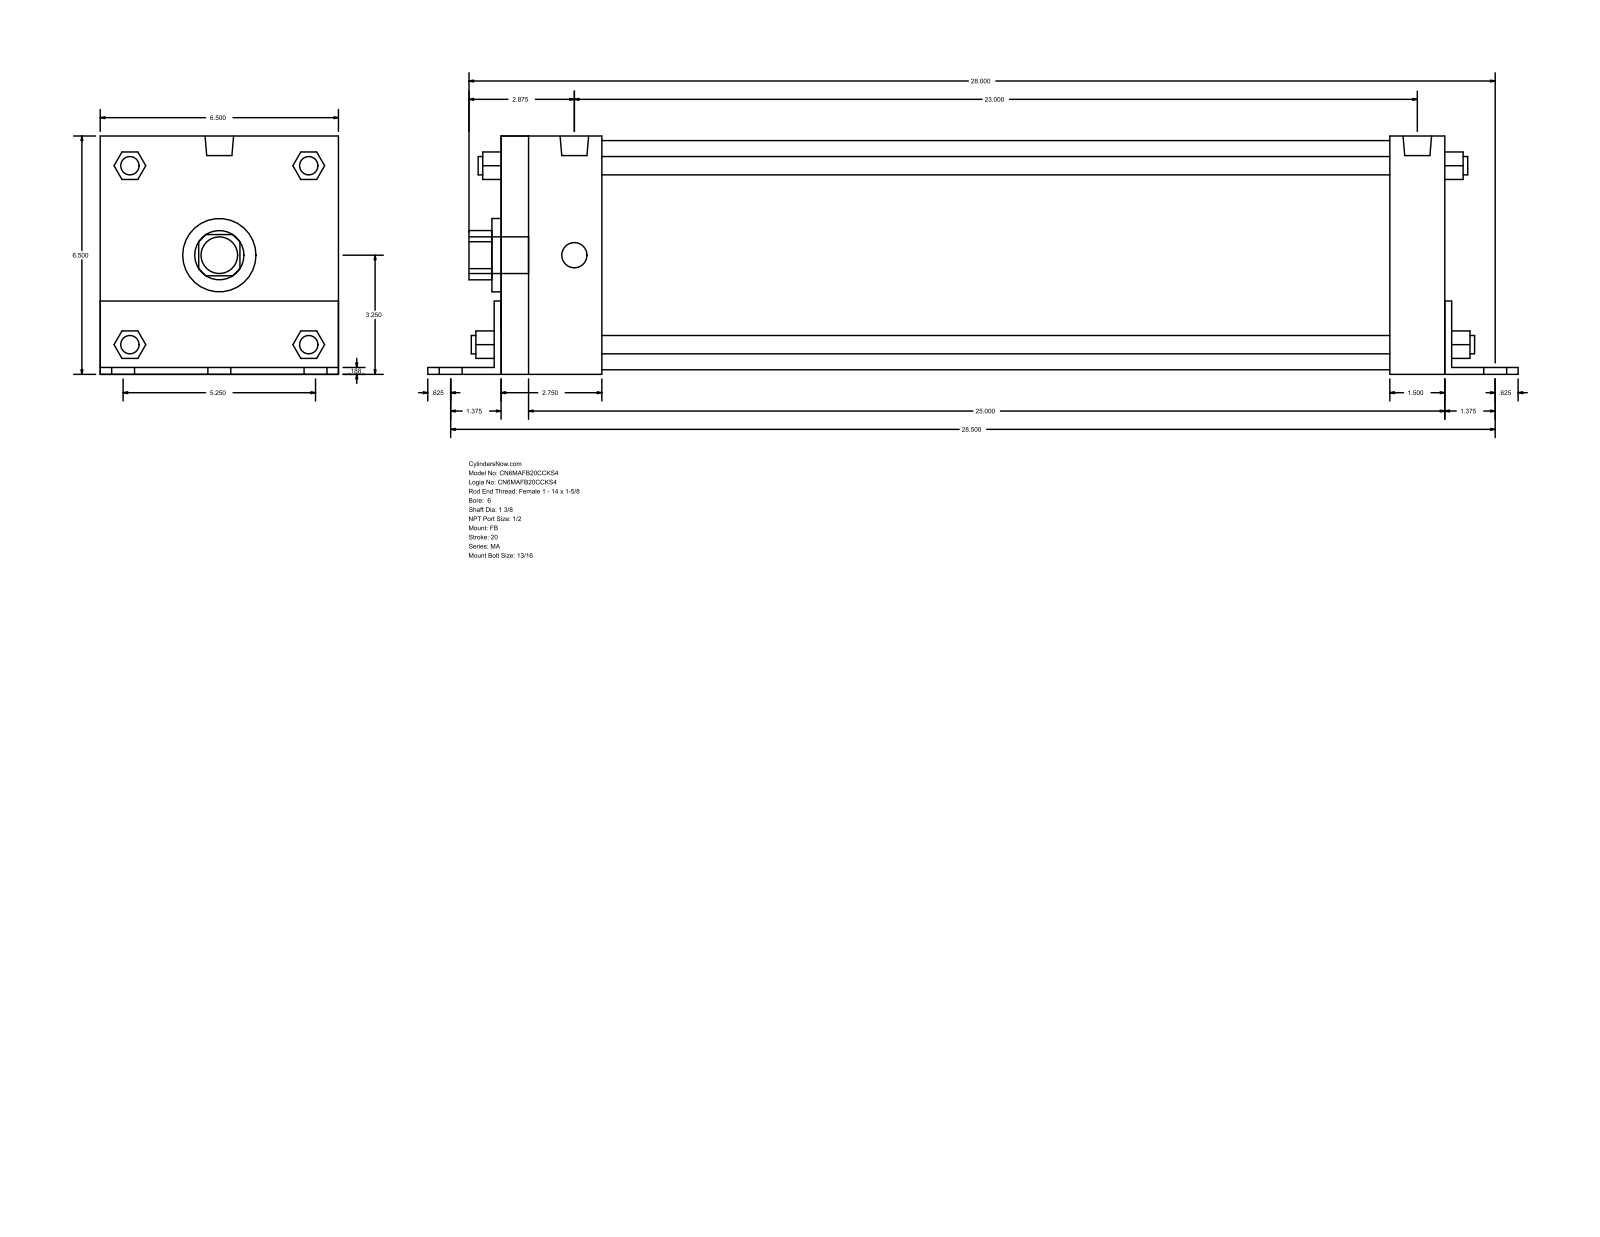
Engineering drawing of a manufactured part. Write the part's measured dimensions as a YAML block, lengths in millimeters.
part_name: "MA_FB__0600_1.375"
step_written_by: "GSSL Pune (CONFIG_CONTROL_DESIGN)"
units: millimeters
bodies: {solids: 0, faces: 140, planar: 105, cylindrical: 35, other: 0}
overall_size: [752.48, 165.15, 165.1]
round_holes:
  - {diameter: 34.92, count: 1}
  - {diameter: 50.8, count: 1}
  - {diameter: 158.75, count: 1}
round_bosses_or_shafts:
  - {diameter: 20.64, count: 6}
  - {diameter: 17.46, count: 4}
  - {diameter: 12.7, count: 4}
  - {diameter: 19.77, count: 2}
  - {diameter: 25.4, count: 1}
partial_cylinders:
  - {radius: 17.06, count: 1}
  - {radius: 32.05, count: 1}
face_to_face_distances: [165.1, 4.76, 650.87, 165.15, 4.71, 160.39, 4.77, 38.1, 655.64, 660.4]
